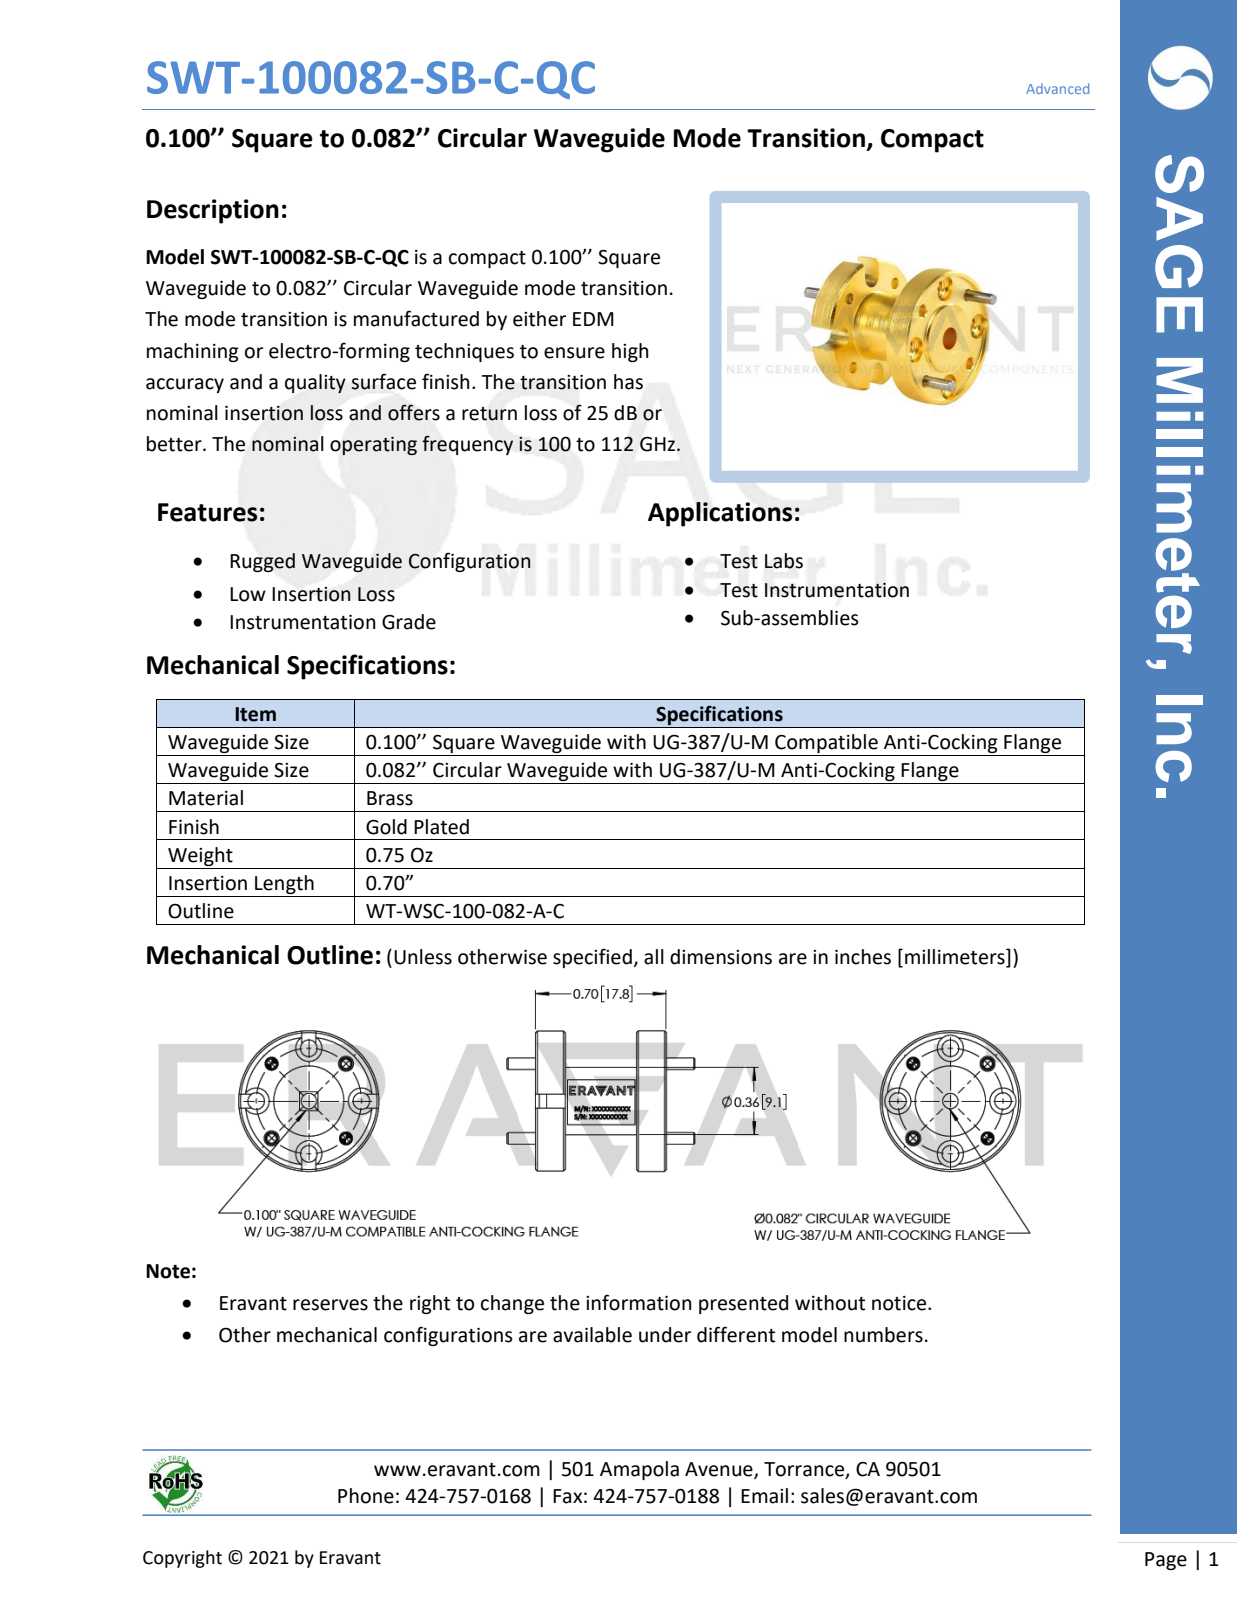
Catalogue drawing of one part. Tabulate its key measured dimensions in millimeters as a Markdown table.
| quantity | value |
| --- | --- |
| part name | WT-WSC-100-082-A-C, Defeatured |
| STEP written by | SolidWorks 2021 (AUTOMOTIVE_DESIGN) |
| units | millimeters |
| bodies | 5 solids, 175 faces (45 planar, 78 cylindrical, 52 other) |
| overall size | 25.5 × 19.1 × 19.1 |
| volume | 2 570 mm³ |
| surface area | 2 223 mm² |
| round holes (diameter × count) | 1.5 × 4, 1.7 × 4, 2.3 × 4, 3.6 × 4, 17.3 × 1 |
| round bosses / shafts (diameter × count) | 1.6 × 4, 19.1 × 1, 9.5 × 1, 9.1 × 1 |
| main face-to-face distances | 3.6, 13.2, 0.5, 4.1, 13.7, 17.3, 9.7, 16.8, 17.8, 1.5 |
| hole center spacings | 5.5, 7.1, 10.1, 13.2, 14.3 |
